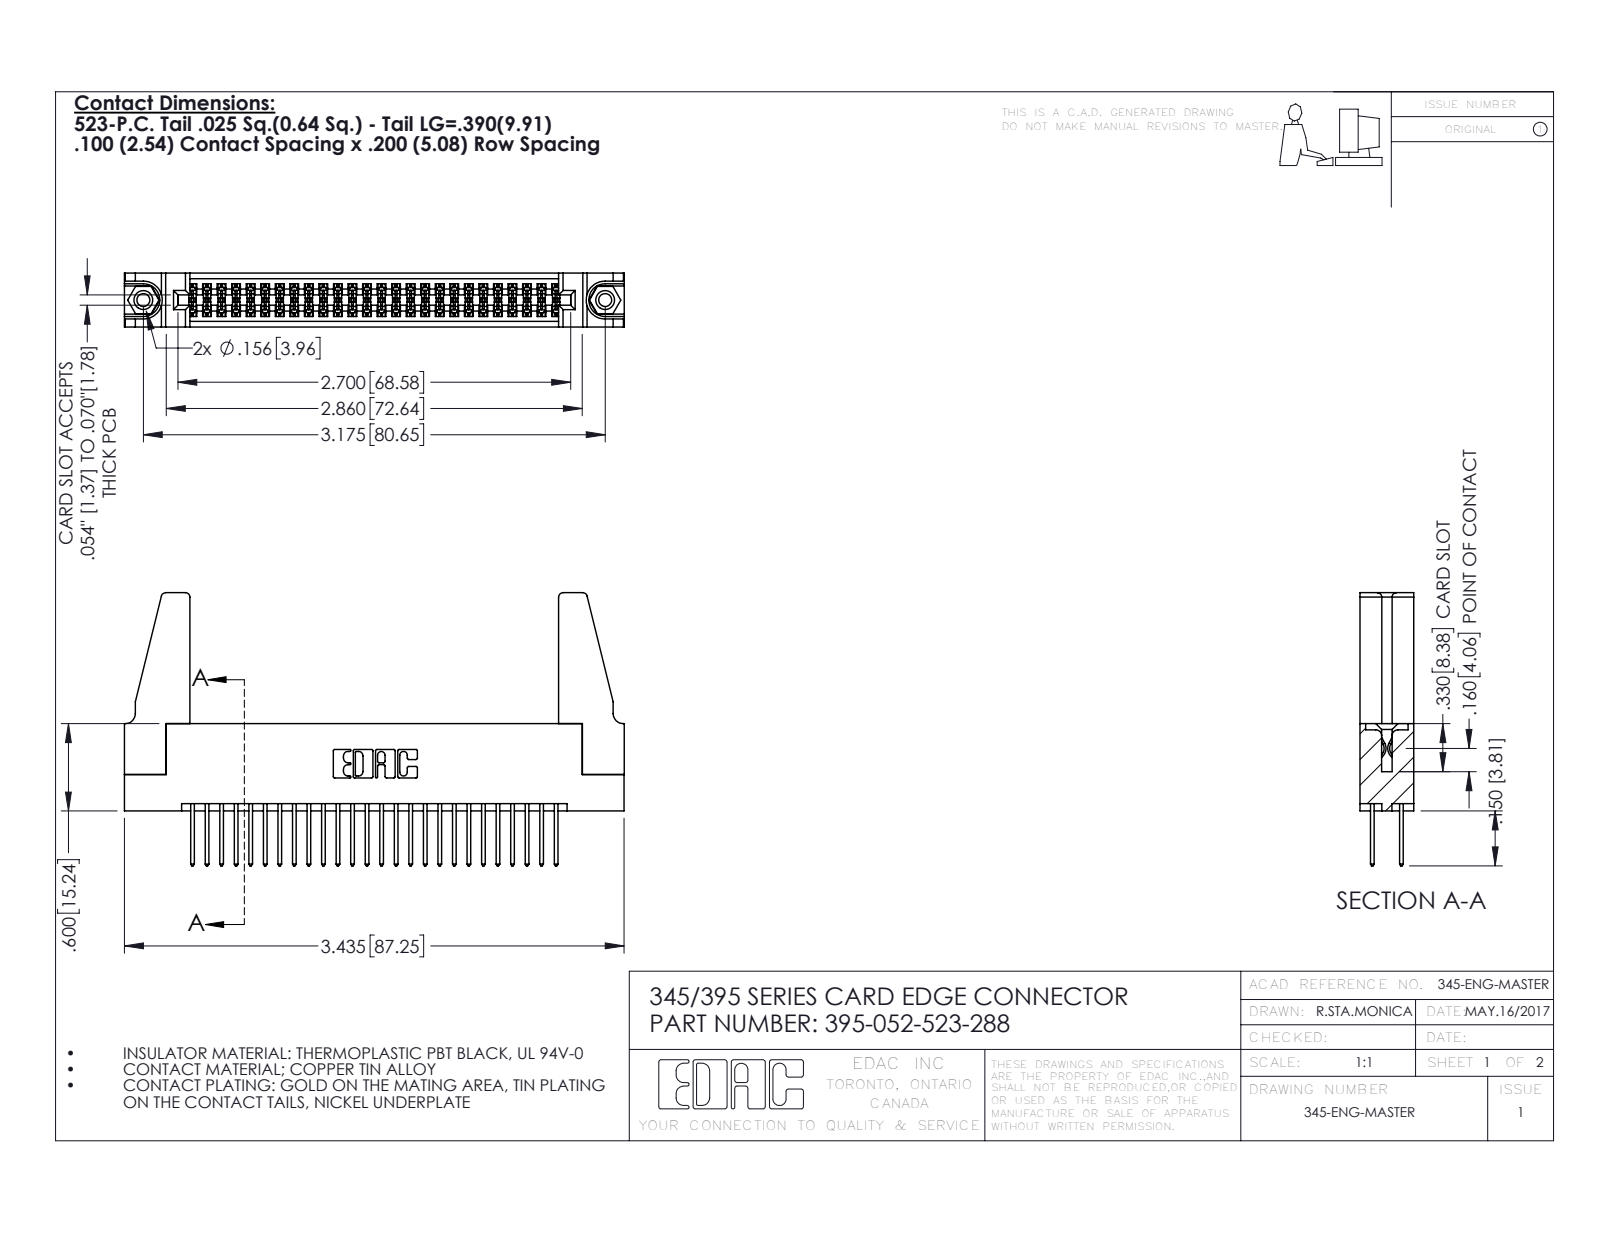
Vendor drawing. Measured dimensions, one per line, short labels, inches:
name: 345-220-078_345-220-088; 345-292-001_345-293-123; 345-250-001_345-250-001-102; 345 Part_Flush Mounting Lugs - 0.156 Dia-TH (+1 more)
written by: SolidWorks 2016 (CONFIG_CONTROL_DESIGN)
unit: in
bodies: 57 solids, 2850 faces (1868 planar, 966 cylindrical, 16 other)
size: 3.436 × 1.877 × 0.37
volume: 0.713 in³; area: 24.43 in²
holes: 2× ⌀0.089, 2× ⌀0.125, 2× ⌀0.156, 1× ⌀0.064
bosses: 2× ⌀0.155
rounds: 78× R0.006, 52× R0.01, 22× R0.01, 8× R0.03, 6× R0.007, 6× R0.031, 3× R0.026, 2× R0.014
face distances: 0.072, 0.298, 0.37, 0.2, 0.098, 0.272, 0.025, 0.225, 0.175, 0.149
hole spacings: 0.27, 2.94, 3.175
